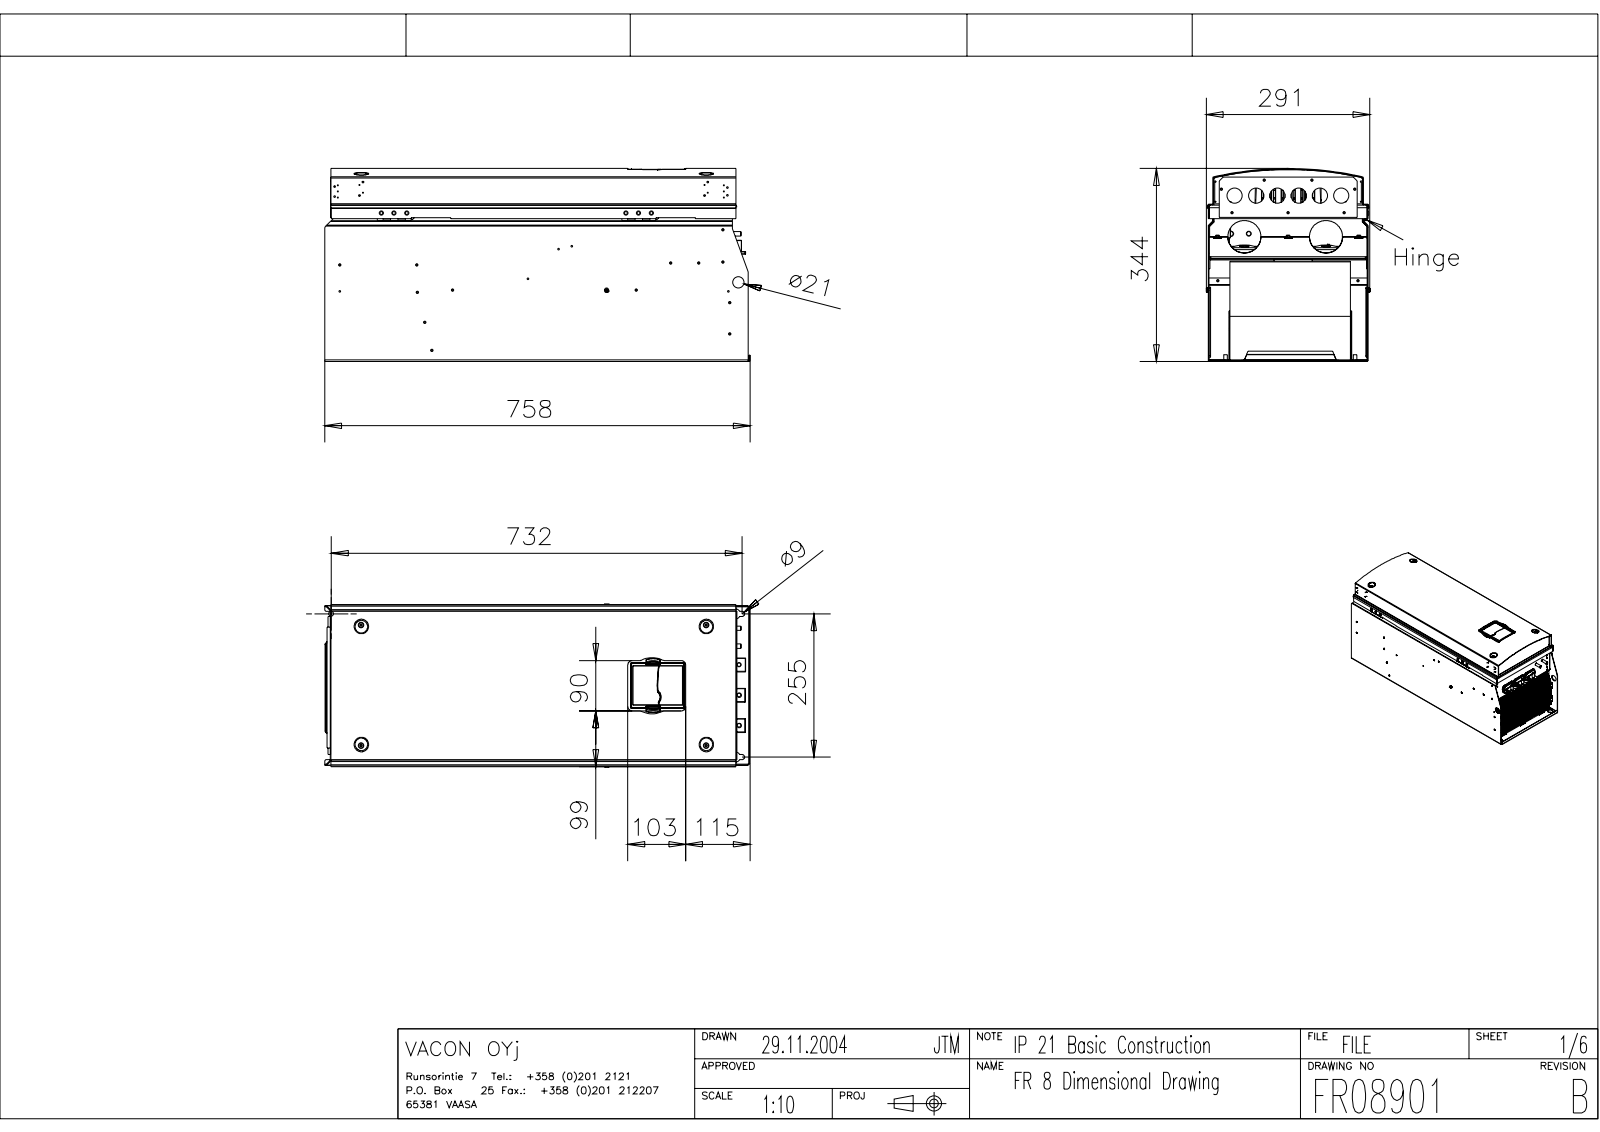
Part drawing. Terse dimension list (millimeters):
name: OUT_NXP_FR8_WITHLCP
written by: CREO PARAMETRIC BY PTC INC, 2018070 (CONFIG_CONTROL_DESIGN)
unit: mm
bodies: 1 solid, 3509 faces (1028 planar, 2236 cylindrical, 245 other)
size: 758.5 × 346.16 × 288.9
holes: 569× ⌀8, 79× ⌀3.4, 26× ⌀4.5, 14× ⌀2, 14× ⌀3.1, 12× ⌀4, 10× ⌀3, 9× ⌀28, 7× ⌀4.2, 6× ⌀0.7, 6× ⌀16, 5× ⌀6
bosses: 4× ⌀5.4, 2× ⌀5.9, 1× ⌀13.5, 1× ⌀3.5, 1× ⌀1.7
rounds: 68× R1, 58× R0.2, 55× R2.5, 18× R0.3, 17× R0.5, 17× R2, 11× R0.1, 9× R3
face distances: 1.5, 1.35, 284.88, 685.9, 47.5, 192.7, 325.72, 324.37, 8.25, 276.75
hole spacings: 9.2, 18.4, 27.6, 36.8, 46, 55.2, 64.4, 73.6
